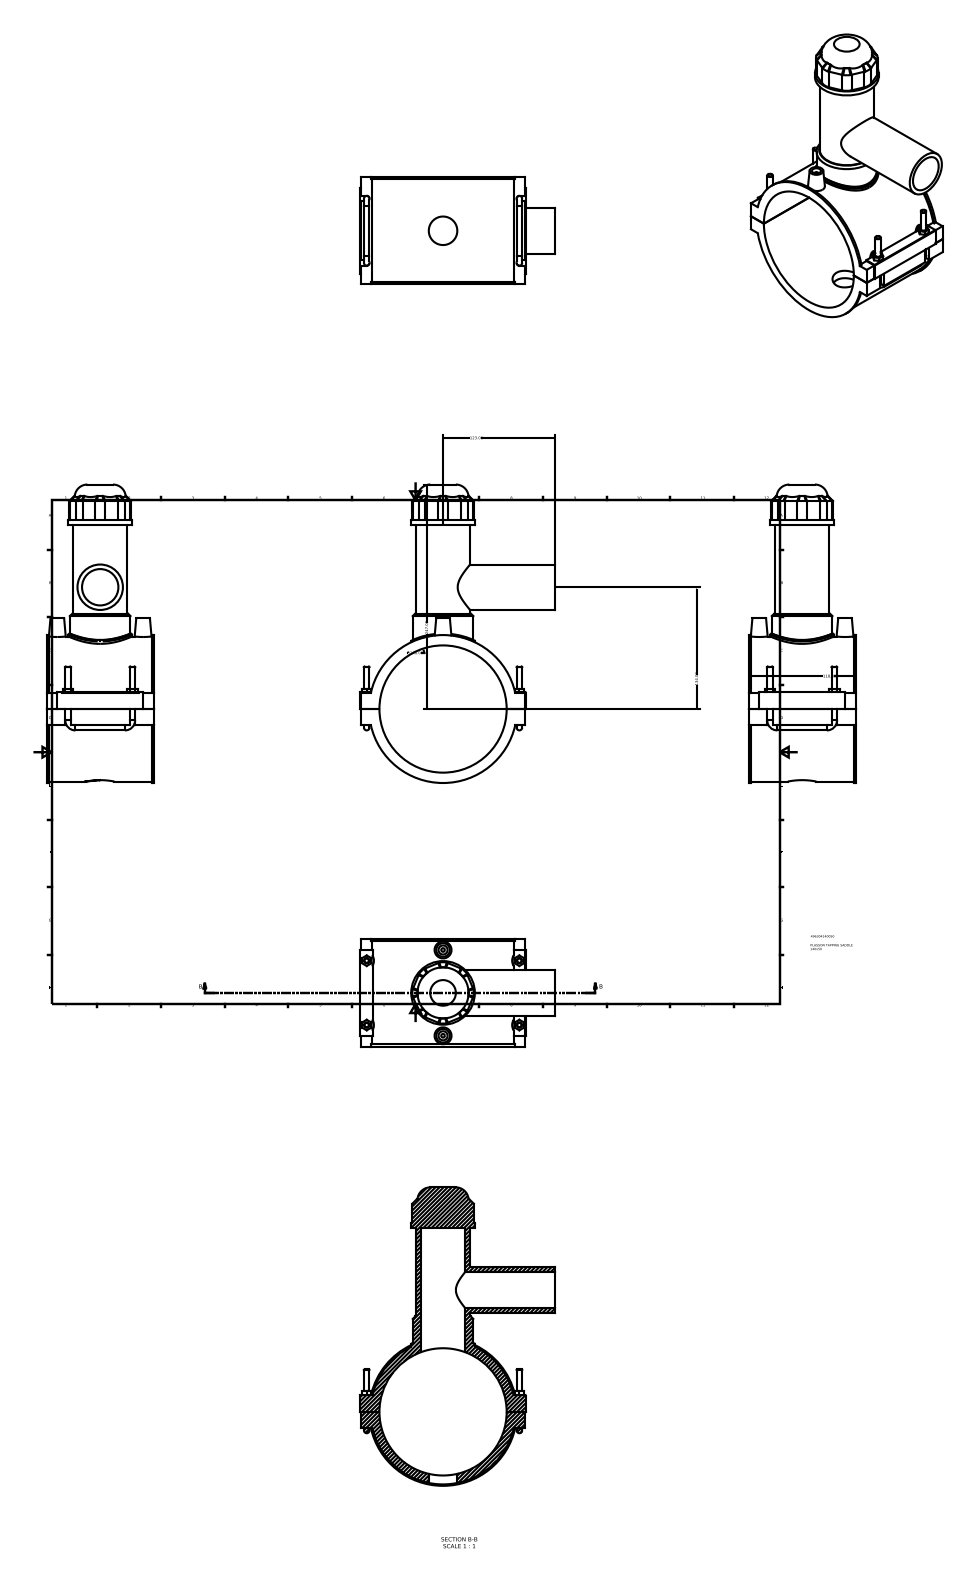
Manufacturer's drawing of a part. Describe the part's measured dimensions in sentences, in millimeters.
The part is named "496304140050". Its 3-D file was written by "Autodesk Inventor 2015 (AUTOMOTIVE_DESIGN)". It is 1 solid with 207 faces: 118 planar, 48 cylindrical and 41 other. Overall it measures 328.4 by 214 by 118 millimeters. Its volume is 956 827 cubic millimeters and its surface area 228 795 square millimeters. Round holes: 2 of diameter 10, 1 of diameter 31.36, 1 of diameter 40, 1 of diameter 49, 1 of diameter 140. Round bosses or shafts: 6 of diameter 6, 2 of diameter 4, 1 of diameter 162.79, 1 of diameter 159.6, 1 of diameter 70, 1 of diameter 66.5, 1 of diameter 59.5, 1 of diameter 50. Partial cylindrical surfaces (rounded edges, fillets, slot ends): 8 of radius 14, 4 of radius 3, 4 of radius 7.5, 1 of radius 0.5, 1 of radius 82.99. The main face-to-face distances are 118, 1, 181, 17.45, 17.55, 202.8, 202.7, 220.25, 180, 36. The hole center spacings are 47.2, 94.4.
